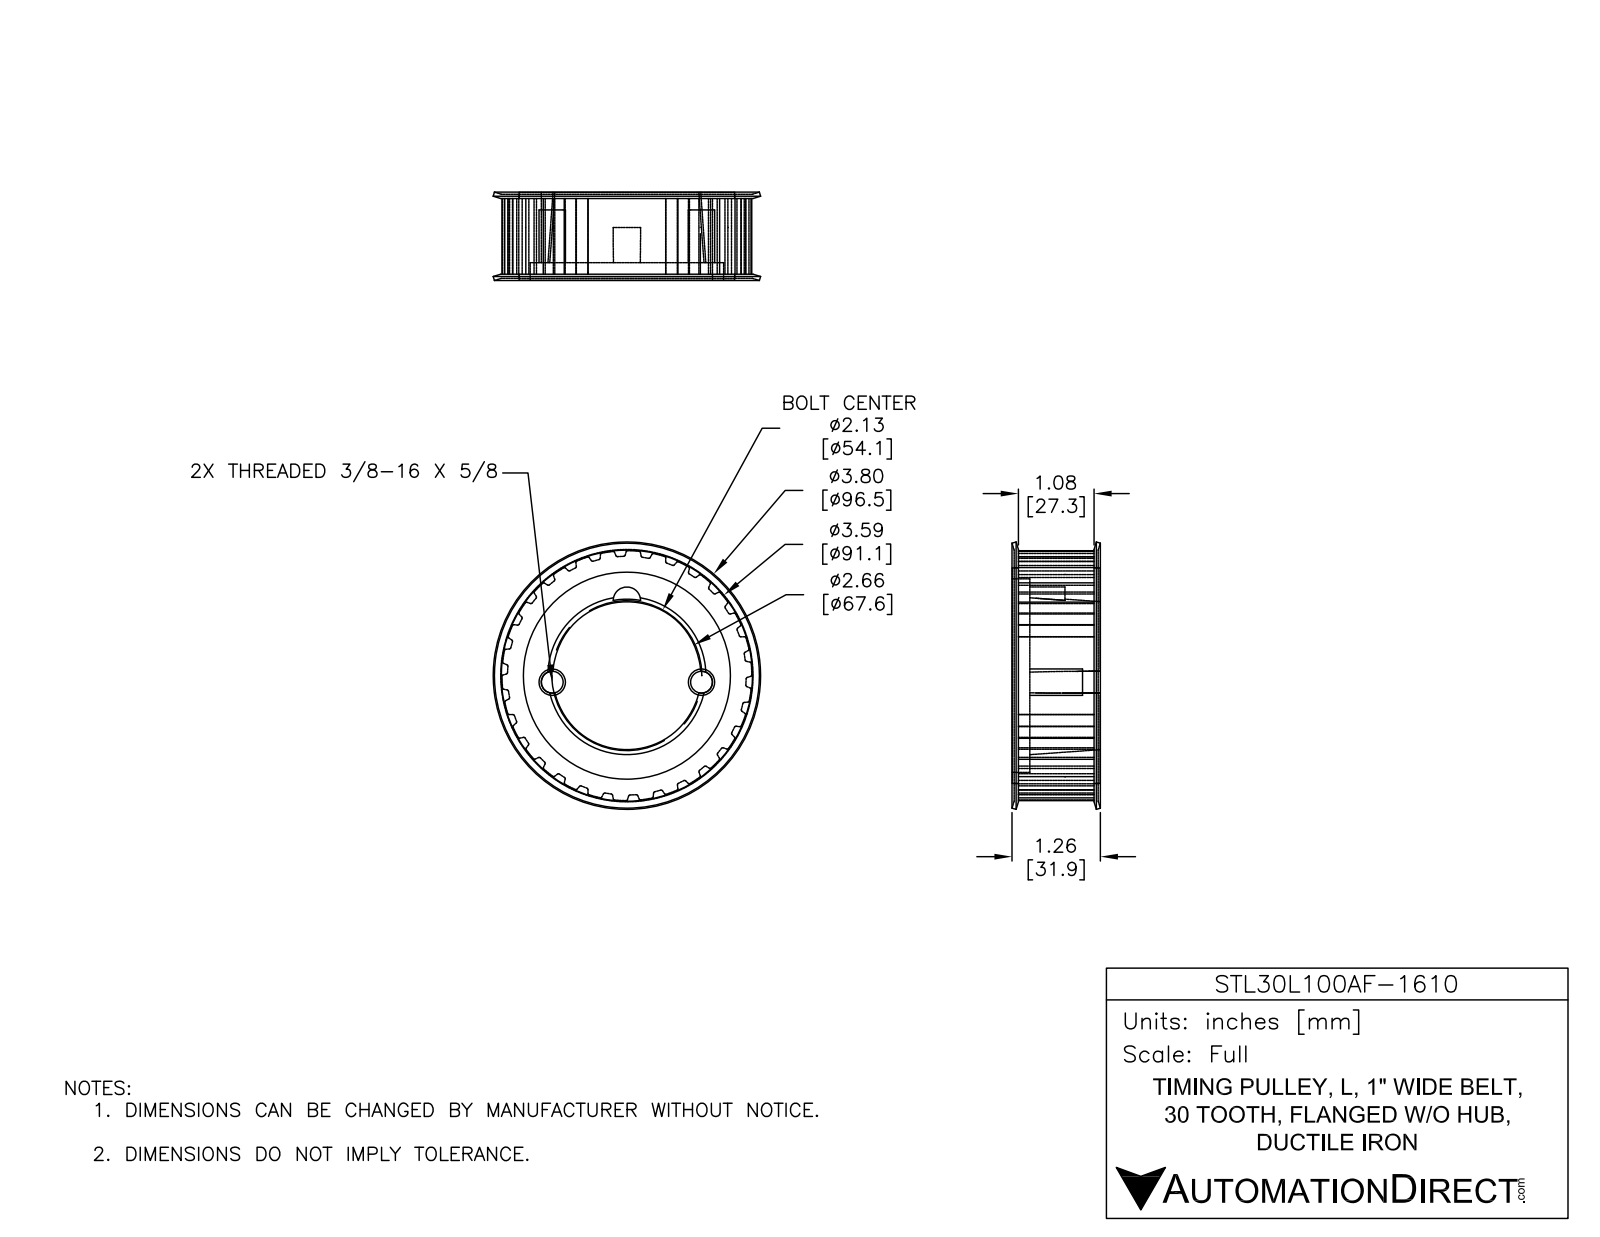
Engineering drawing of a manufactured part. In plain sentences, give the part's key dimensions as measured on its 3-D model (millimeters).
The part is named "STL30L100AF-1610". Its 3-D file was written by "SolidWorks 2018 (AUTOMOTIVE_DESIGN)". It is 4 solids with 307 faces: 100 planar, 189 cylindrical and 18 other. Overall it measures 96.52 by 96.52 by 31.88 millimeters. Its volume is 110 923 cubic millimeters and its surface area 49 603 square millimeters. Round holes: 1 of diameter 69.85, 1 of diameter 77.79, 1 of diameter 77.9. Partial cylindrical surfaces (rounded edges, fillets, slot ends): 60 of radius 0.38, 60 of radius 0.51, 2 of radius 3.94, 1 of radius 4.95, 1 of radius 45.1. The main face-to-face distances are 27.31, 2.22, 29.53, 0.7, 31.06, 1.52, 28.83, 30.36, 28.84, 1.53.
